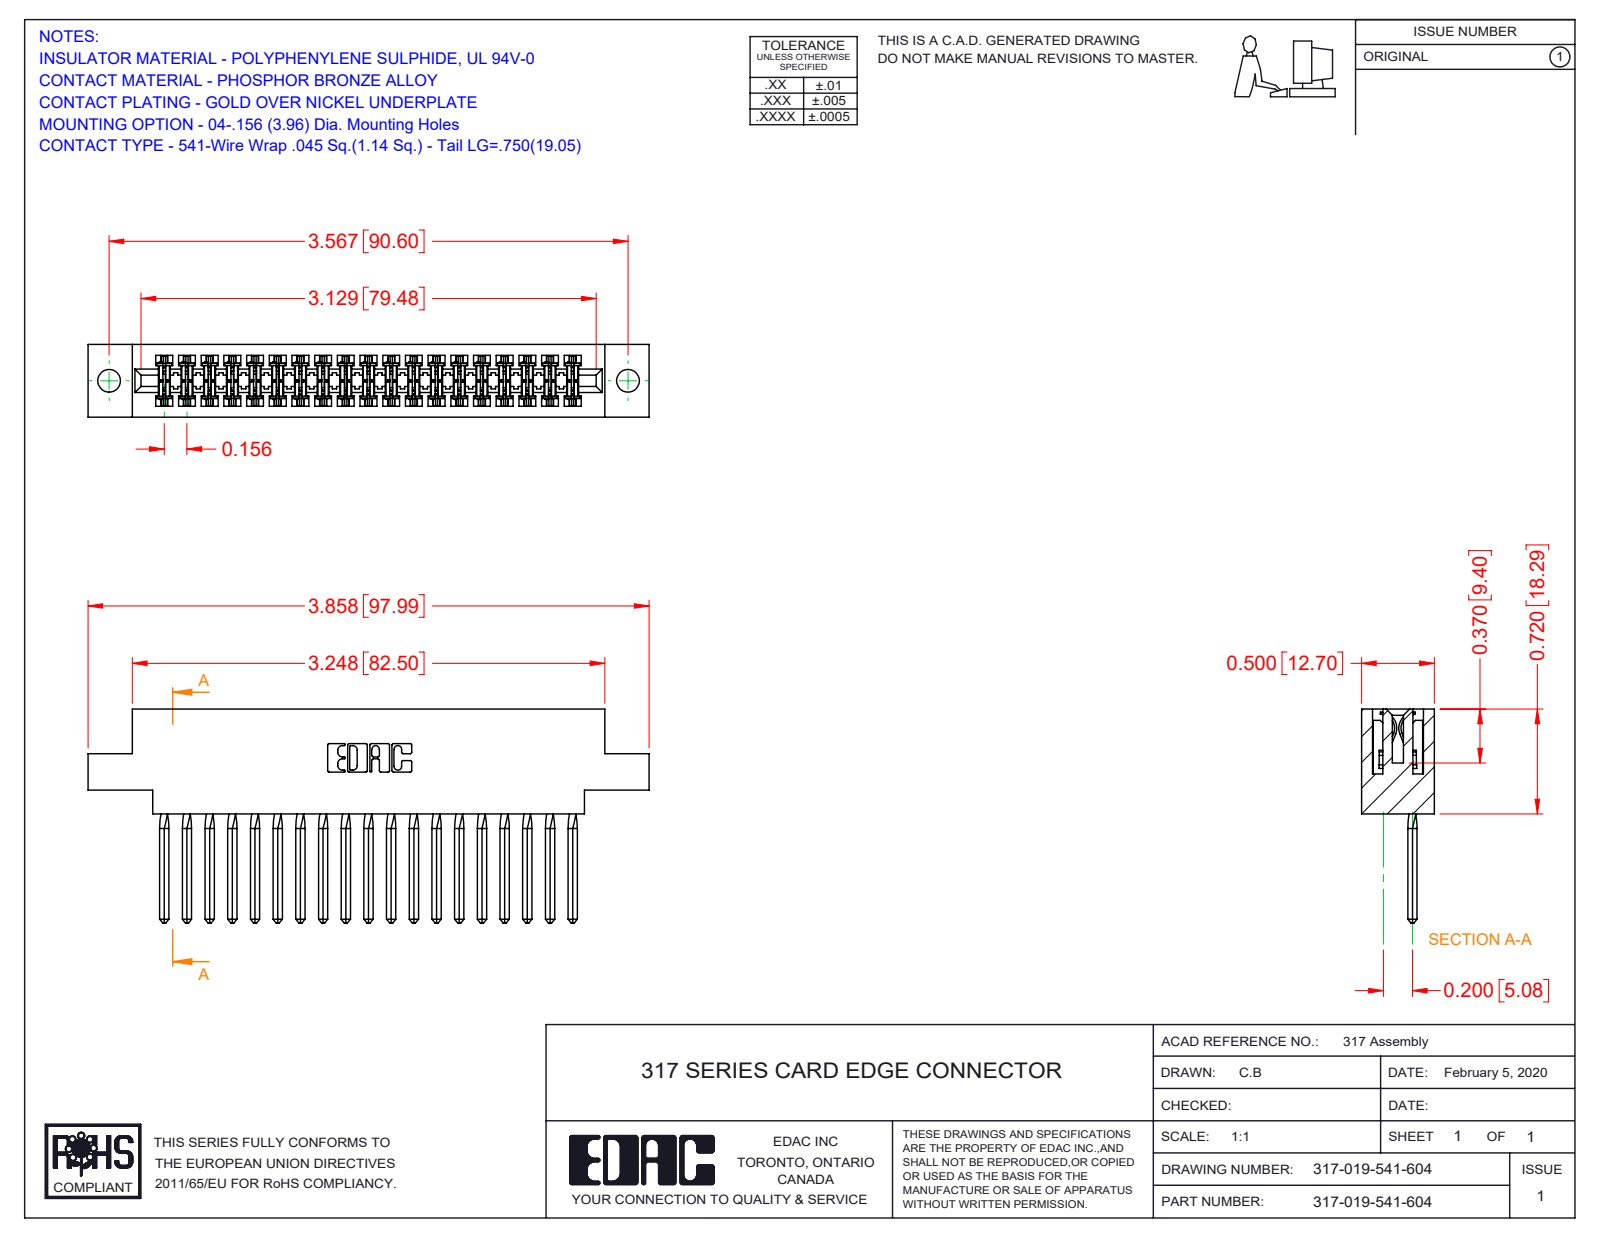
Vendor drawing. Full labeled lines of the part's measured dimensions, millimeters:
Part name (STEP PRODUCT): 317-019-541-604; 317-290-002_541; 317 Part_.156 Dia - TH
STEP written by: SolidWorks 2016 (CONFIG_CONTROL_DESIGN)
Units: millimetres
Bodies: 20 solids, 2990 faces (2414 planar, 500 cylindrical, 76 other)
Overall size (bounding box): 98 × 37.3 × 12.7
Volume: 15 100 mm³ · Surface area: 20 380 mm²
Round holes (diameter × count): ⌀4 ×2
Partial cylindrical surfaces — rounded edges, fillets, slot ends (radius × count): R0.4 ×38, R0.3 ×22, R0.2 ×6, R0.8 ×6, R0.7 ×3, R2.4 ×2, R2.5 ×2, R2.8 ×2
Main face-to-face distances: 12.7, 1.9, 10.8, 2.8, 8.9, 5, 19.6, 5.6, 16.8, 18.3
Hole centre spacings: 90.6
